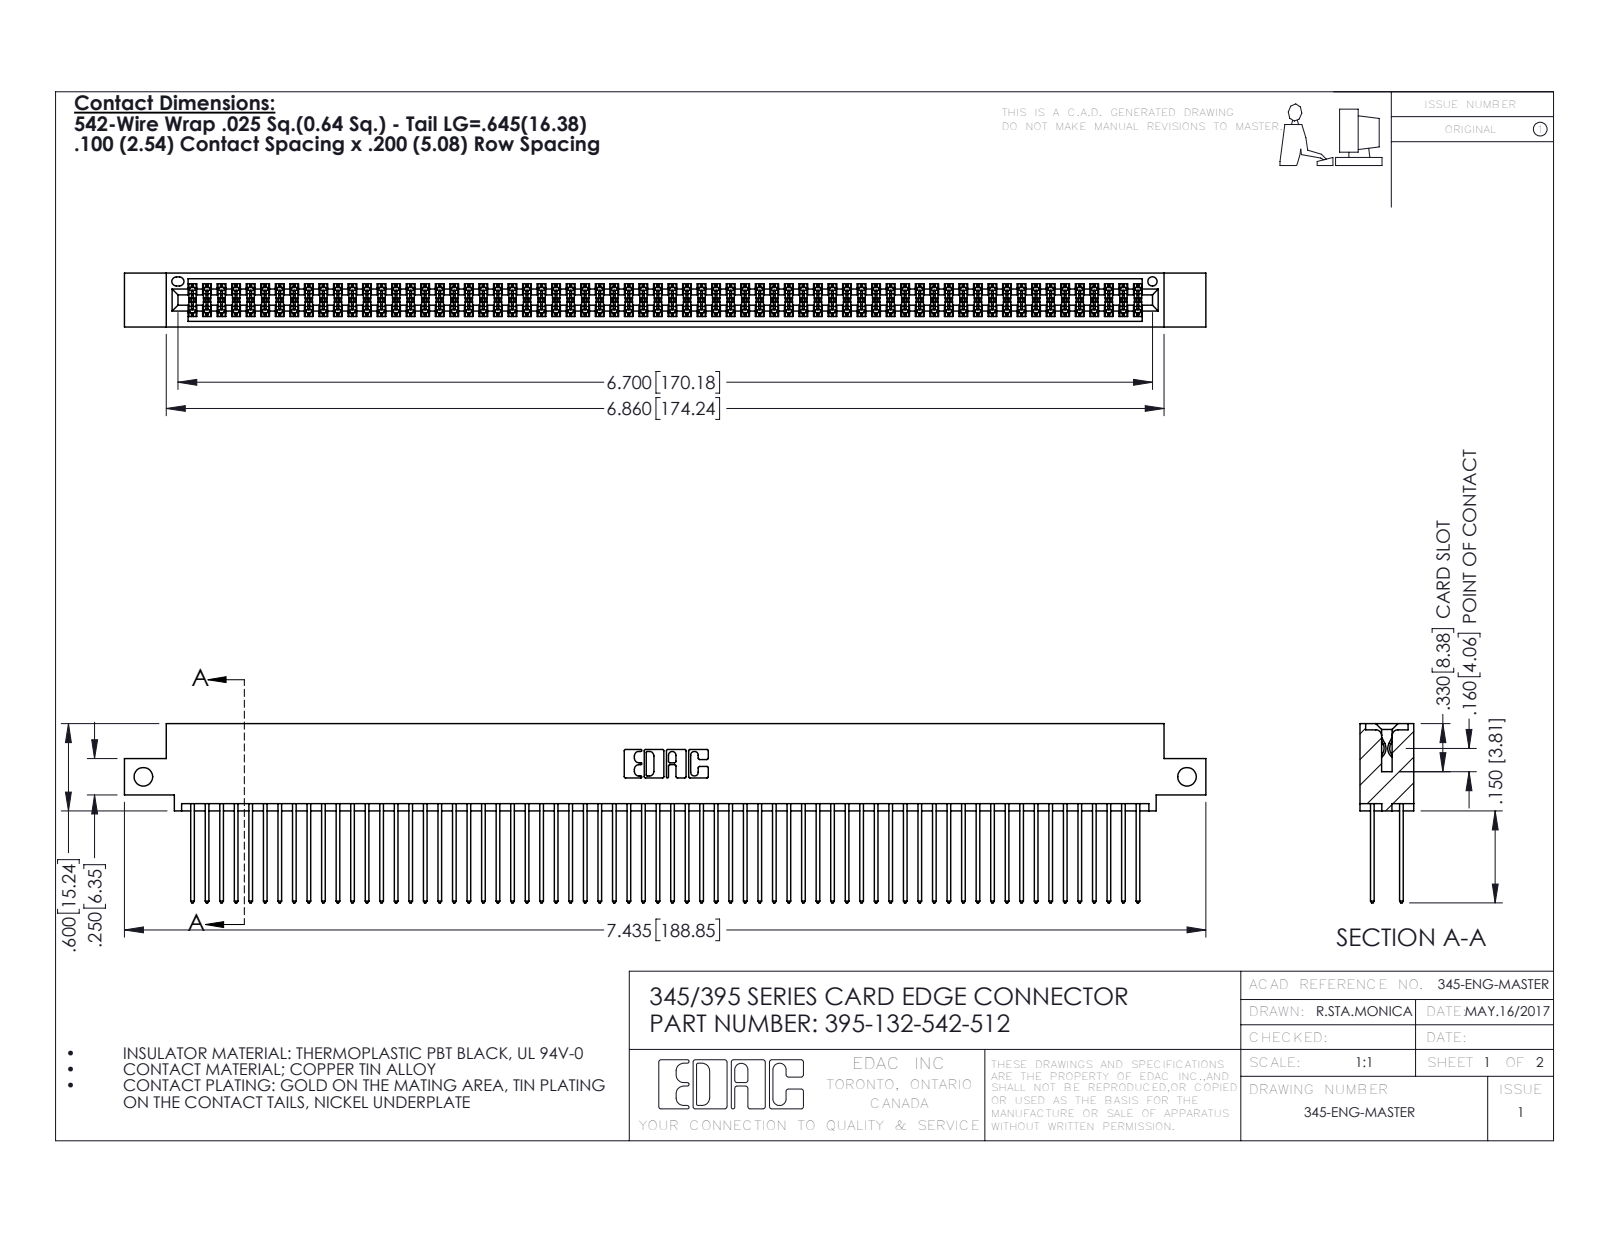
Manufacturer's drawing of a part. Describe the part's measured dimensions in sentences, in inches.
The part is named "345-292-001_345-293-142; 345 Part_0.110 Offset - Side Mount; 395-132-542-512". Its 3-D file was written by "SolidWorks 2016 (CONFIG_CONTROL_DESIGN)". It is 133 solids with 6730 faces: 4440 planar, 2290 cylindrical and 0 other. Overall it measures 7.435 by 1.232 by 0.37 inches. Its volume is 1.161 cubic inches and its surface area 48.69 square inches. Round holes: 2 of diameter 0.128, 1 of diameter 0.064. Partial cylindrical surfaces (rounded edges, fillets, slot ends): 198 of radius 0.006, 132 of radius 0.01, 22 of radius 0.01, 6 of radius 0.007, 6 of radius 0.031, 3 of radius 0.026, 2 of radius 0.014, 2 of radius 0.019. The main face-to-face distances are 0.298, 0.072, 0.2, 0.098, 0.272, 0.025, 0.225, 0.37, 0.175, 0.149. The hole center spacings are 7.175.
